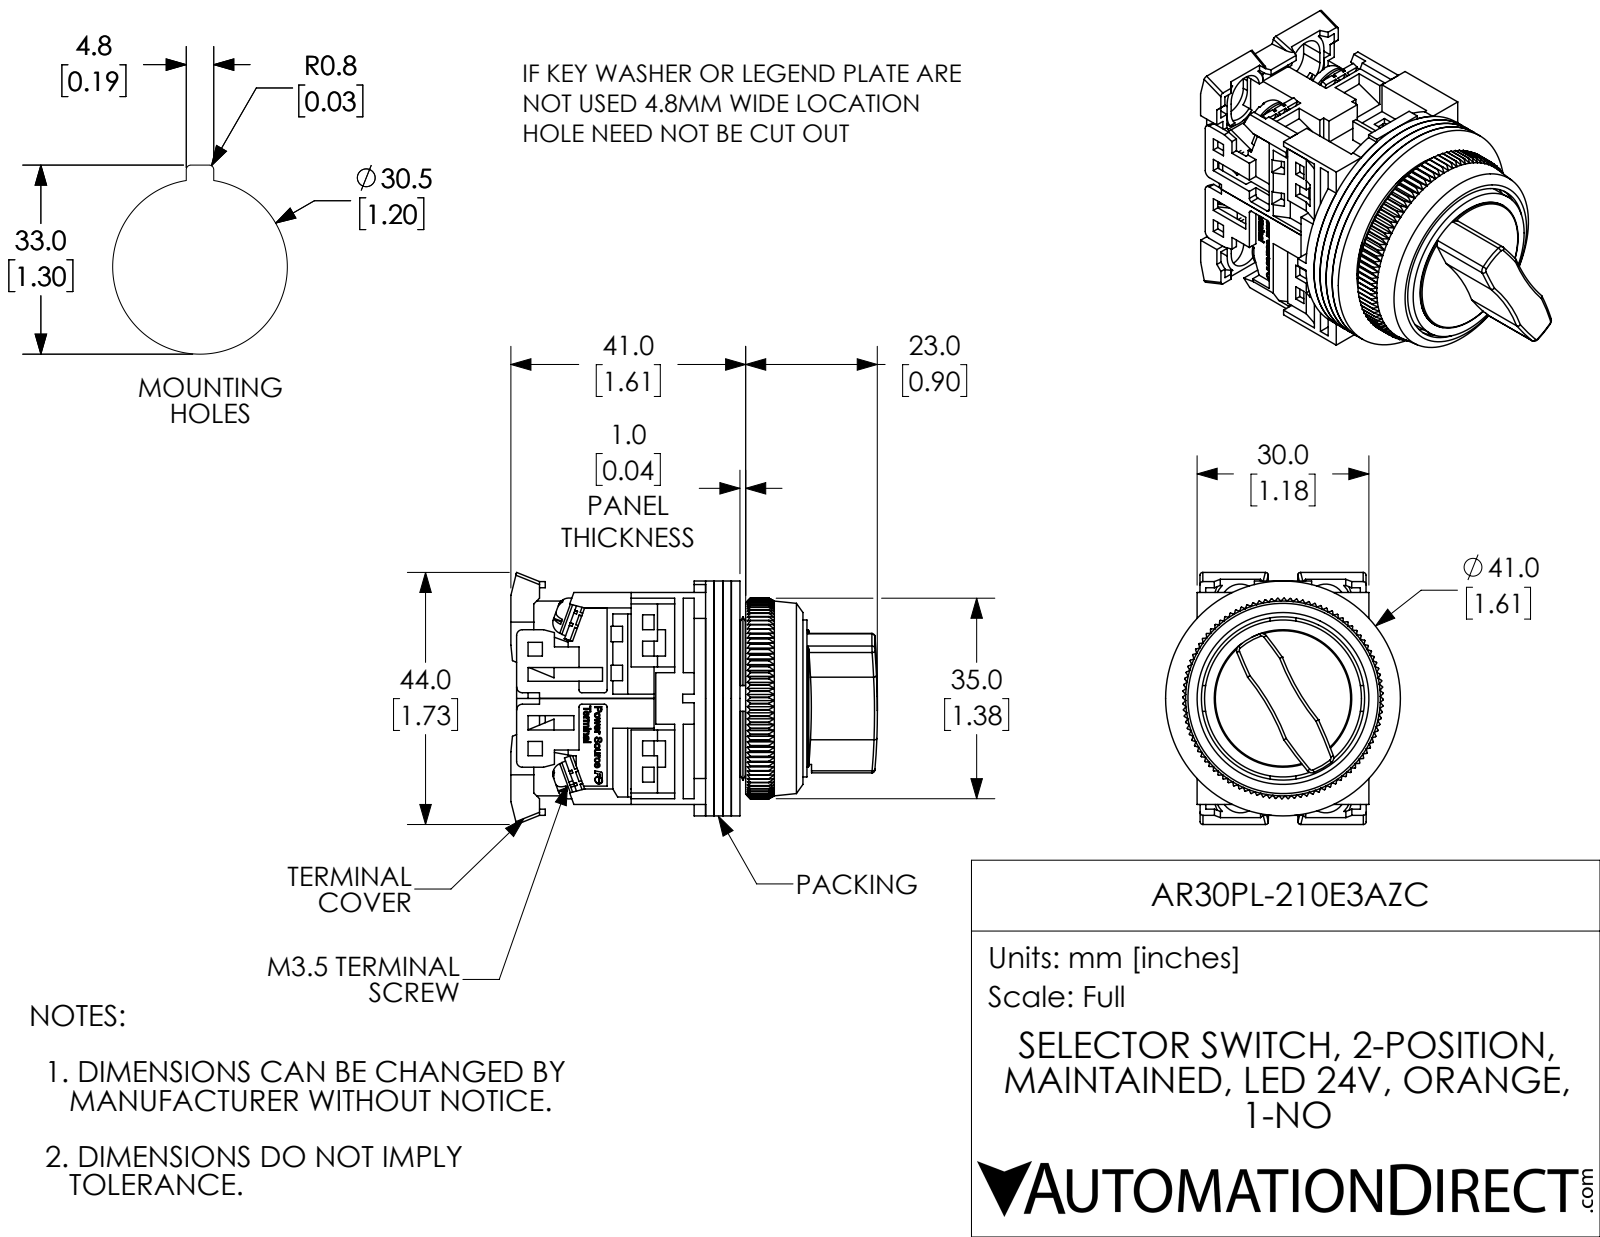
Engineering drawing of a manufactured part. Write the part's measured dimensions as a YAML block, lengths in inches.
part_name: "AR30PL-210E3AZC"
step_written_by: "SolidWorks 2017 (AUTOMOTIVE_DESIGN)"
units: inches
bodies: {solids: 25, faces: 2434, planar: 1731, cylindrical: 305, other: 398}
overall_size: [2.52, 1.732, 1.614]
volume: 2.238
surface_area: 59.31
round_holes:
  - {diameter: 0.138, count: 8}
  - {diameter: 0.142, count: 4}
  - {diameter: 0.118, count: 1}
  - {diameter: 0.472, count: 1}
  - {diameter: 0.709, count: 1}
  - {diameter: 0.768, count: 1}
  - {diameter: 0.827, count: 1}
  - {diameter: 1.122, count: 1}
  - {diameter: 1.181, count: 1}
  - {diameter: 1.252, count: 1}
round_bosses_or_shafts:
  - {diameter: 0.26, count: 4}
  - {diameter: 0.138, count: 4}
  - {diameter: 0.063, count: 2}
  - {diameter: 1.614, count: 1}
  - {diameter: 1.15, count: 1}
  - {diameter: 1.079, count: 1}
  - {diameter: 0.945, count: 1}
  - {diameter: 0.886, count: 1}
partial_cylinders:
  - {radius: 0.059, count: 16}
  - {radius: 0.02, count: 12}
  - {radius: 0.039, count: 8}
  - {radius: 0.138, count: 4}
  - {radius: 0.177, count: 4}
  - {radius: 0.118, count: 2}
  - {radius: 1.575, count: 2}
  - {radius: 2.953, count: 2}
face_to_face_distances: [0.059, 0.118, 0.177, 0.039, 0.079, 1.417, 1.358, 0.811, 0.197, 0.02]
hole_center_spacings: [0.579, 0.61]
